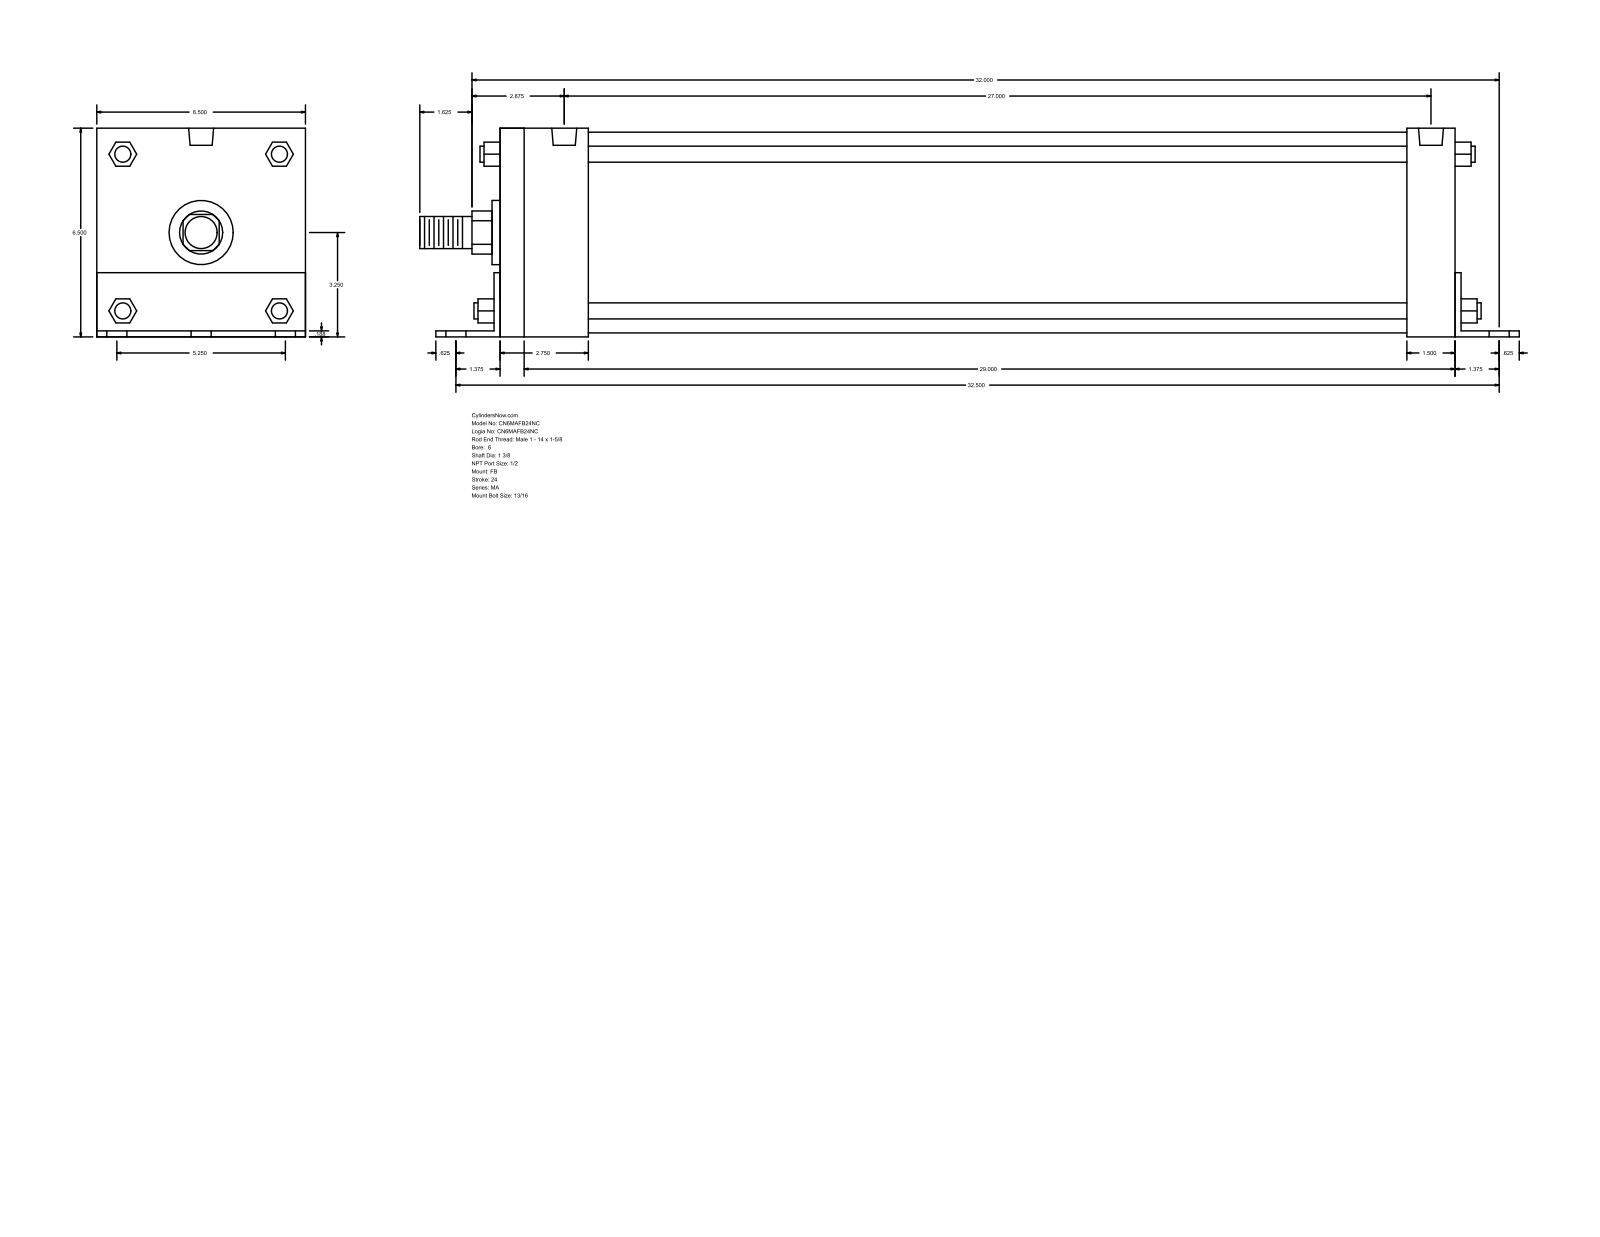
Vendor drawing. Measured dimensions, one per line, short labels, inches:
name: MA_FB__0600_1.375
written by: GSSL Pune (CONFIG_CONTROL_DESIGN)
unit: in
bodies: 0 solids, 140 faces (105 planar, 35 cylindrical, 0 other)
size: 34.125 × 6.502 × 6.5
holes: 6× ⌀0.813, 4× ⌀0.687, 2× ⌀0.778
bosses: 4× ⌀0.5, 1× ⌀6.25, 1× ⌀2, 1× ⌀1.375, 1× ⌀1
rounds: 1× R0.672, 1× R1.262
face distances: 6.5, 0.187, 29.625, 6.502, 0.185, 6.315, 0.188, 1.5, 1.687, 30
hole spacings: 2.625, 32.481, 32.375, 3.3, 3.377, 4.276, 5.25, 26.875
